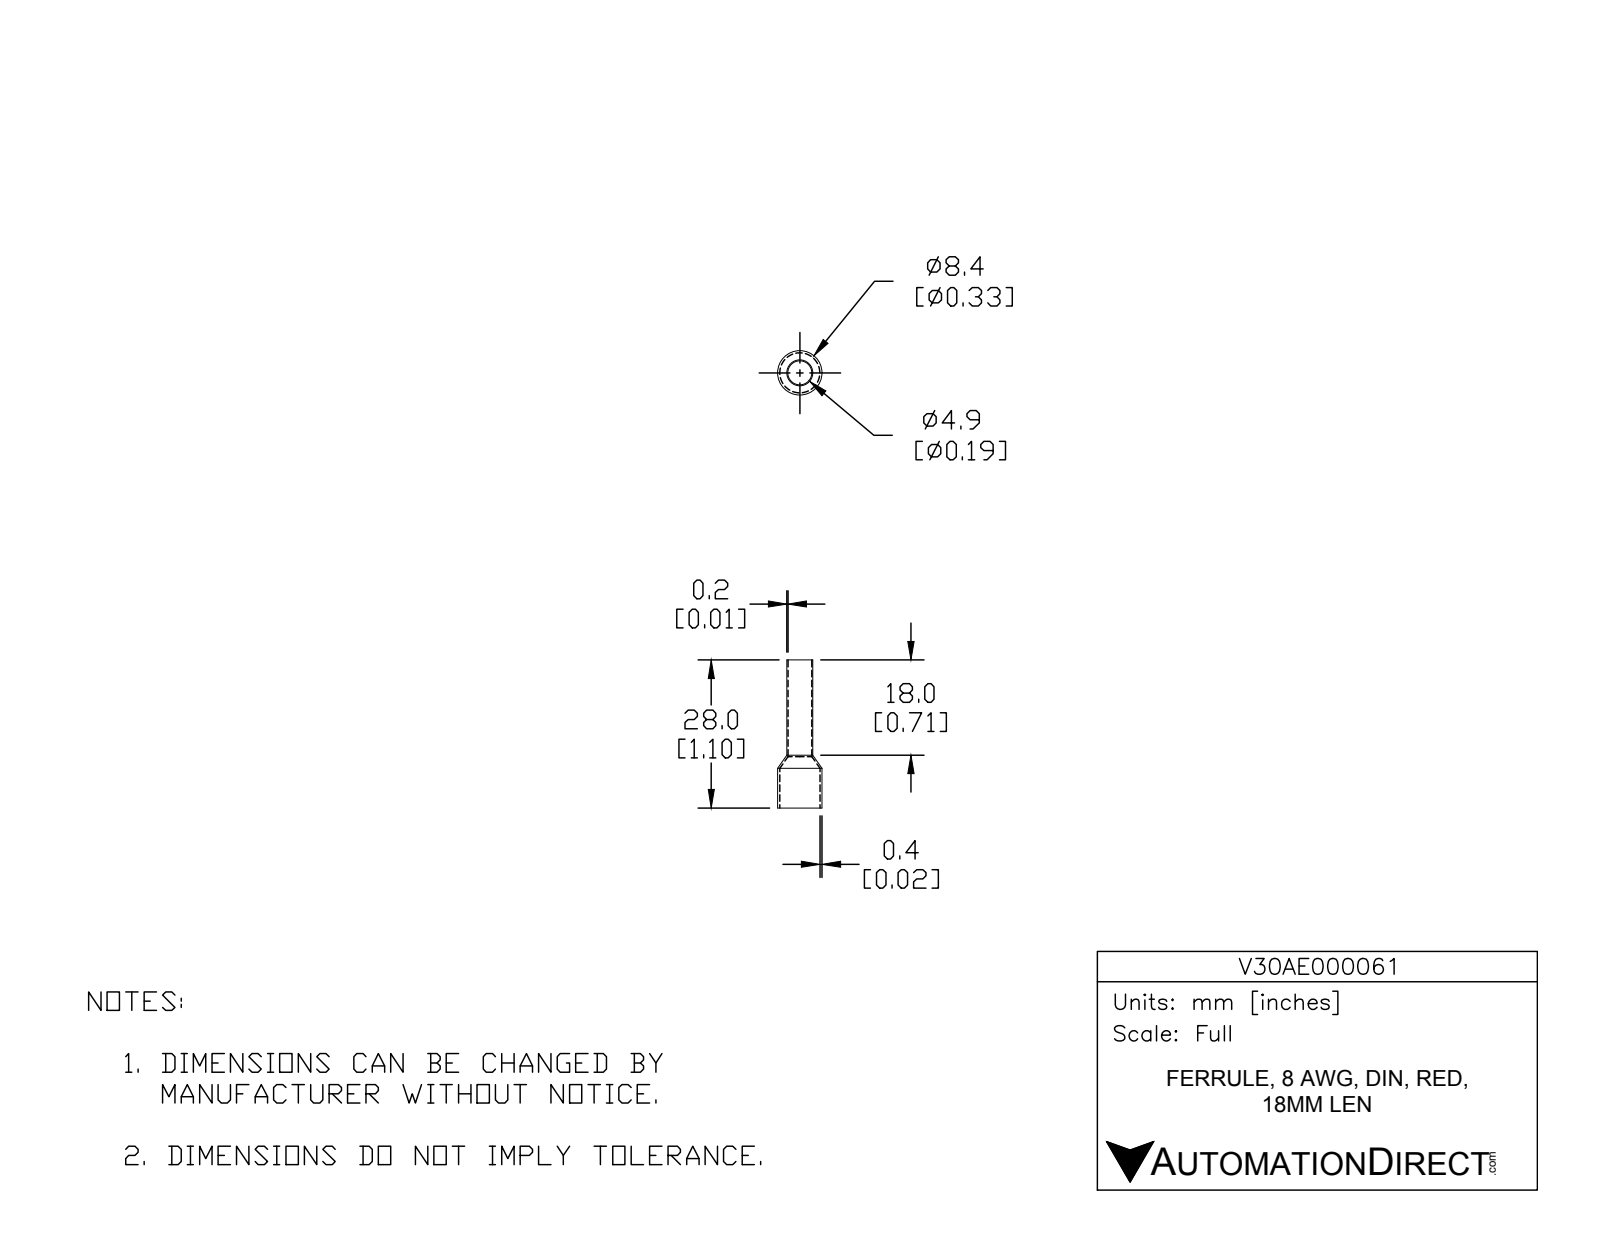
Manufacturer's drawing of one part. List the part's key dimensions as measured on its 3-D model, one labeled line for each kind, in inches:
Part name (STEP PRODUCT): V30AE000061
STEP written by: SolidWorks 2017 (AUTOMOTIVE_DESIGN)
Units: inches
Bodies: 1 solid, 14 faces (2 planar, 8 cylindrical, 4 other)
Overall size (bounding box): 1.102 × 0.331 × 0.331
Volume: 0.009 in³ · Surface area: 1.614 in²
Round holes (diameter × count): ⌀0.177 ×1, ⌀0.299 ×1
Round bosses / shafts (diameter × count): ⌀0.331 ×1, ⌀0.193 ×1
Main face-to-face distances: 1.102
